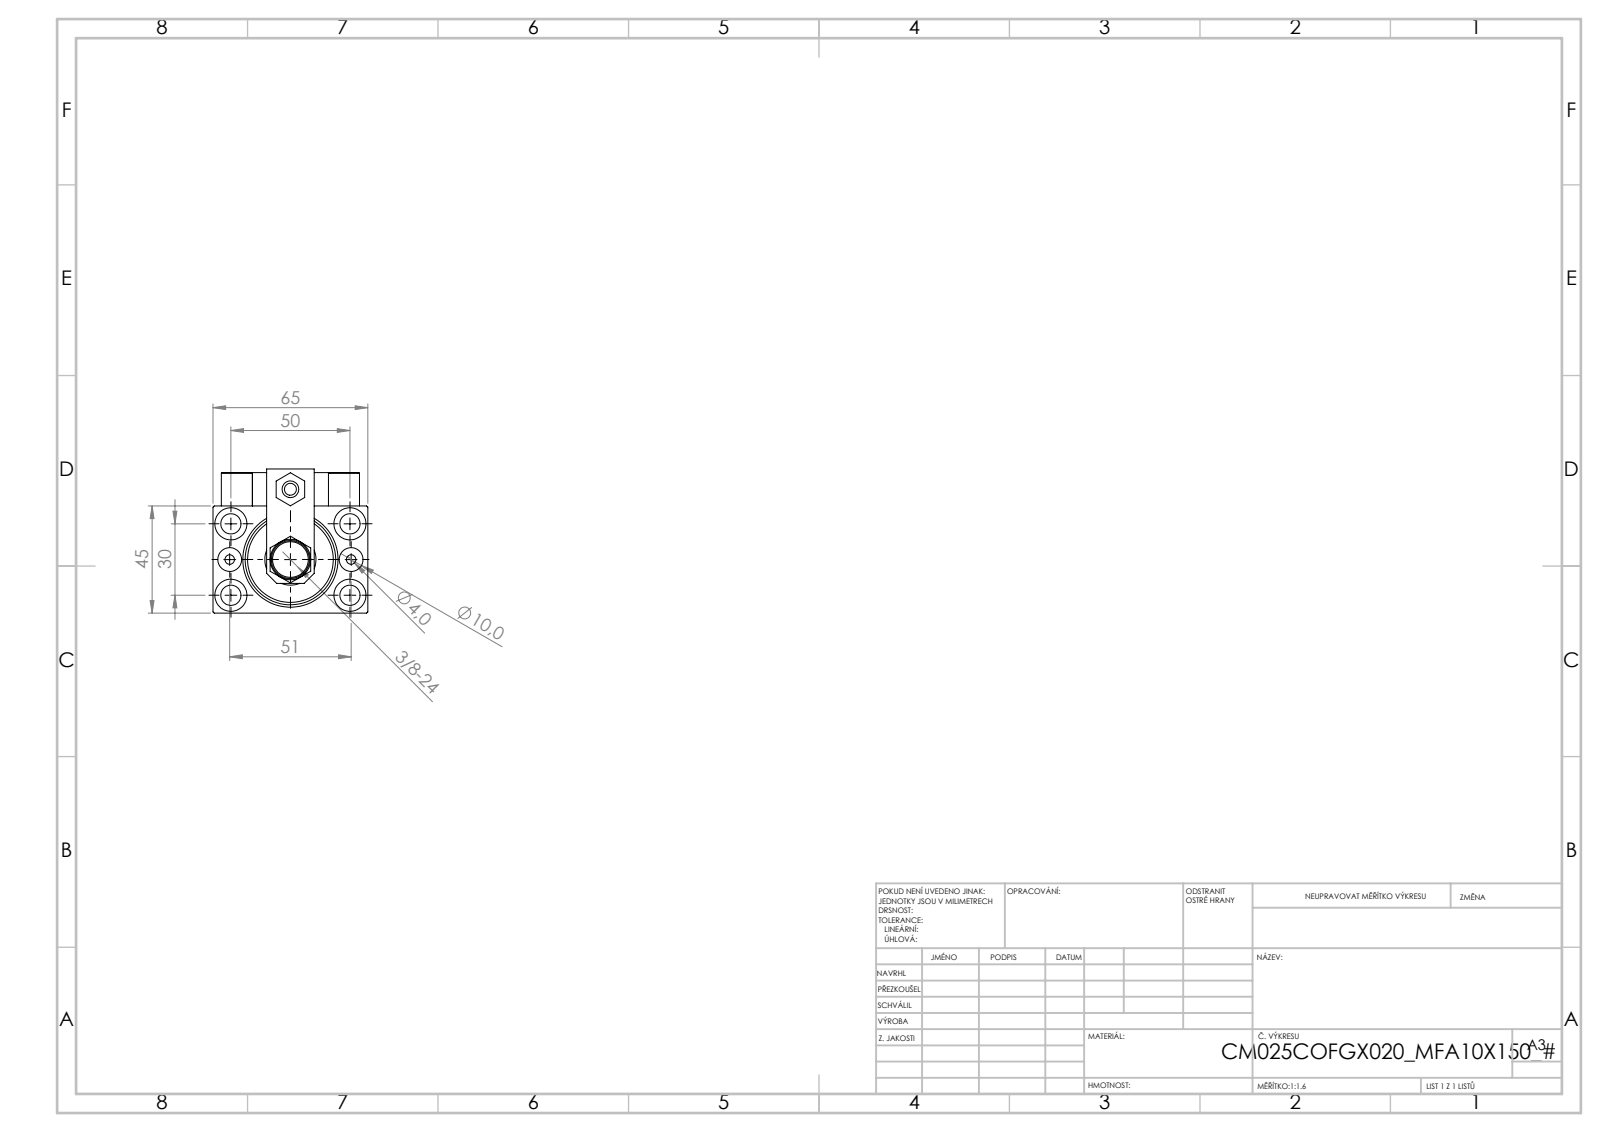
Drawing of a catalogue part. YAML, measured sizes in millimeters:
part_name: "ALLEN BOLT D5; TYC_L79; V450CM_C_Body; SWITCH DIM B,W (+7 more)"
step_written_by: "SolidWorks 2019 (CONFIG_CONTROL_DESIGN)"
units: millimeters
bodies: {solids: 24, faces: 1330, planar: 576, cylindrical: 188, other: 566}
overall_size: [163, 65, 60.5]
volume: 229358
surface_area: 72034
round_holes:
  - {diameter: 4, count: 6}
  - {diameter: 8, count: 5}
  - {diameter: 8.5, count: 5}
  - {diameter: 3.2, count: 4}
  - {diameter: 13.5, count: 4}
  - {diameter: 5, count: 2}
  - {diameter: 10, count: 2}
  - {diameter: 7, count: 1}
  - {diameter: 14.5, count: 1}
  - {diameter: 18, count: 1}
  - {diameter: 21.5, count: 1}
  - {diameter: 25, count: 1}
round_bosses_or_shafts:
  - {diameter: 5, count: 2}
  - {diameter: 3.8, count: 2}
  - {diameter: 16, count: 1}
  - {diameter: 13, count: 1}
  - {diameter: 11, count: 1}
  - {diameter: 10, count: 1}
partial_cylinders:
  - {radius: 0.3, count: 30}
  - {radius: 3, count: 2}
  - {radius: 8.5, count: 1}
face_to_face_distances: [45, 65, 59, 14, 6, 3, 19, 5, 7, 81]
hole_center_spacings: [15.01, 29.15, 52.68, 11.37, 20, 22.09, 25.5, 28.9]
